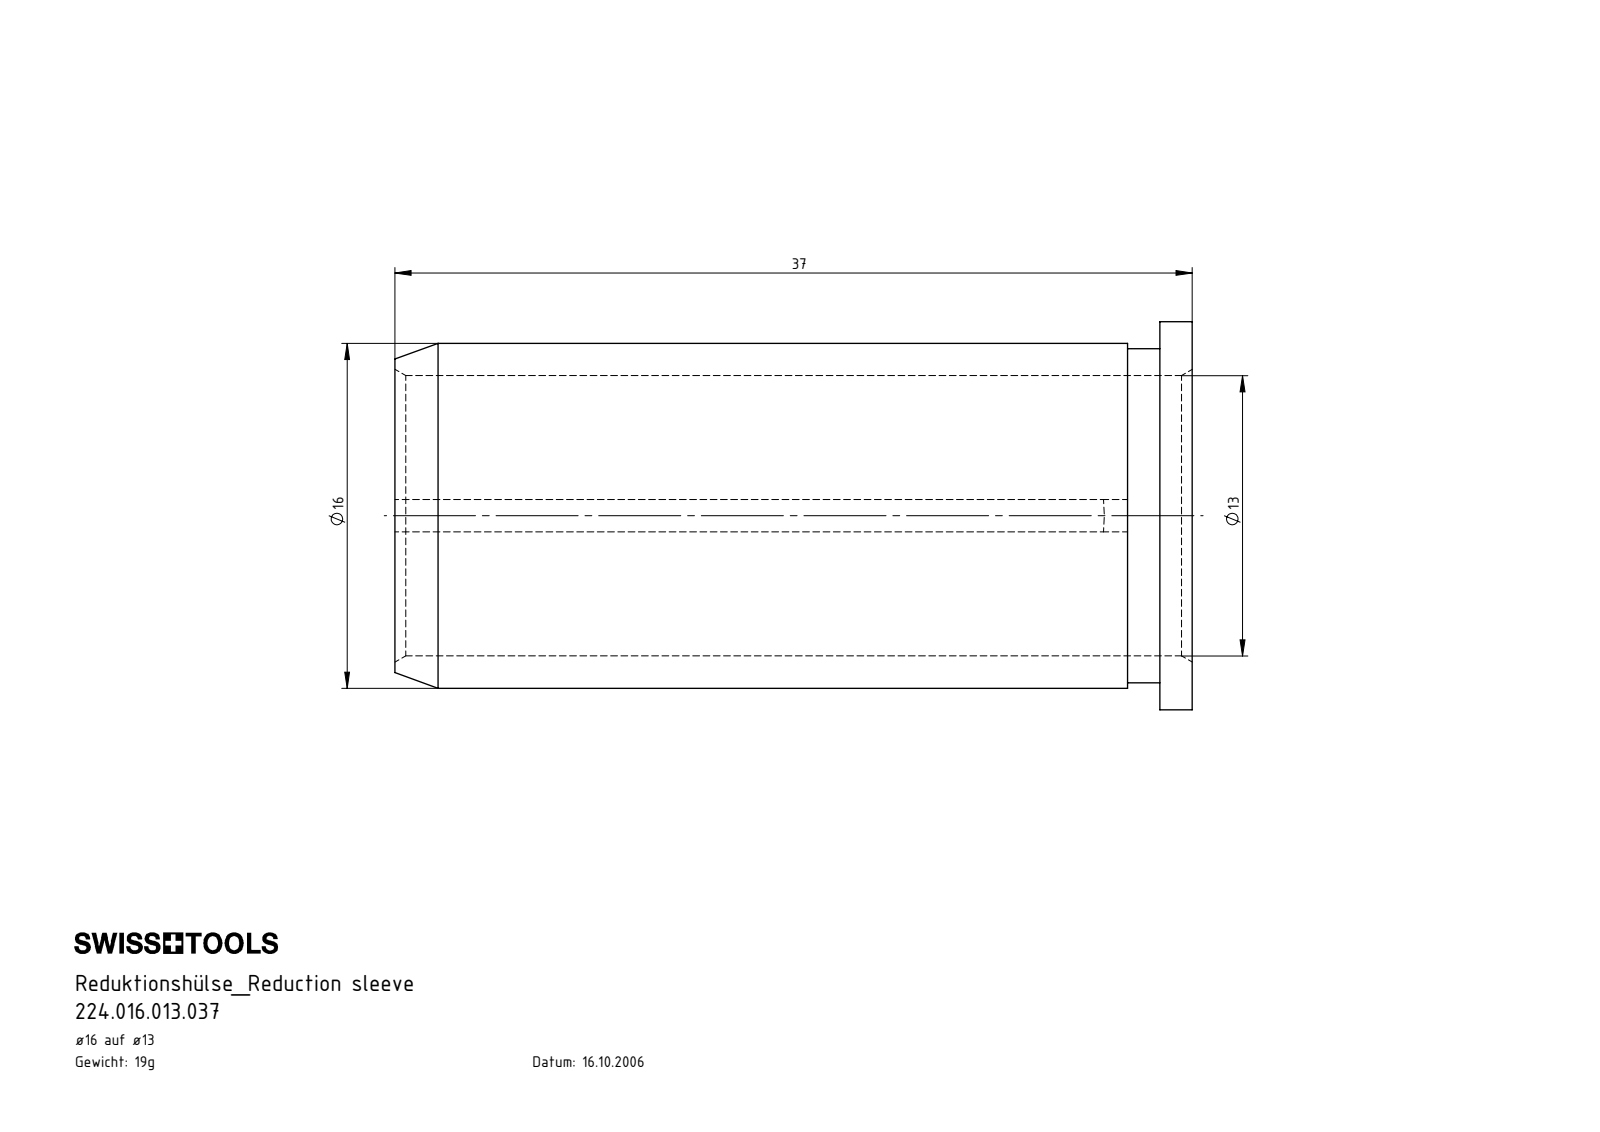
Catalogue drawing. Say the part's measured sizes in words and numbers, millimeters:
The part is named "U13.U16.001.037". Its 3-D file was written by "SolidWorks 2017 (AUTOMOTIVE_DESIGN)". It is 1 solid with 14 faces: 6 planar, 5 cylindrical and 3 other. Overall it measures 37 by 18 by 18 millimeters. Its volume is 2 474 cubic millimeters and its surface area 3 596 square millimeters. Round holes: 1 of diameter 13. Round bosses or shafts: 1 of diameter 18, 1 of diameter 16, 1 of diameter 15.5. Partial cylindrical surfaces (rounded edges, fillets, slot ends): 1 of radius 31.5. The main face-to-face distances are 1.5, 35.5, 37, 34, 3.
